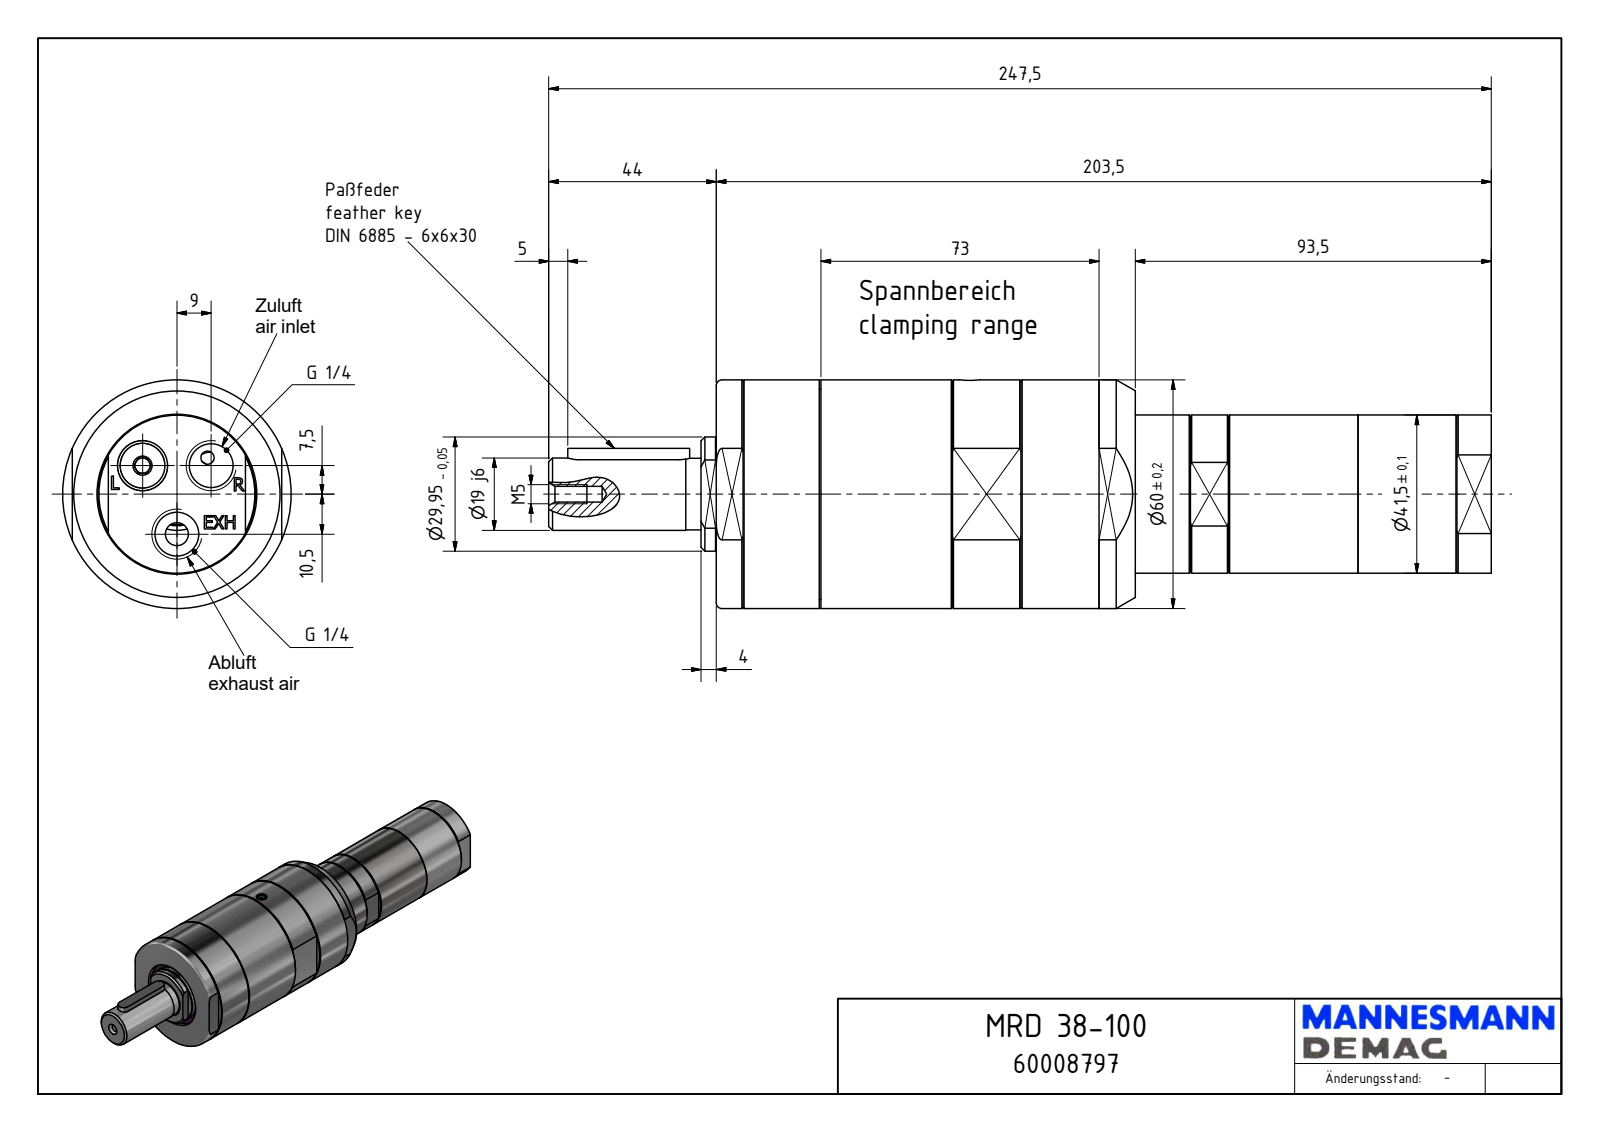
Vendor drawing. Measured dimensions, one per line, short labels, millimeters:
name: MRD 38-100_60008797
written by: Autodesk Inventor 2018 (AUTOMOTIVE_DESIGN)
unit: mm
bodies: 1 solid, 215 faces (125 planar, 41 cylindrical, 49 other)
size: 247.5 × 60 × 60
volume: 443 336 mm³; area: 45 818 mm²
holes: 3× ⌀11.45, 2× ⌀4, 1× ⌀1.55, 1× ⌀4.13, 1× ⌀5.5, 1× ⌀35, 1× ⌀42
bosses: 1× ⌀60, 1× ⌀55.18, 1× ⌀41.5, 1× ⌀39, 1× ⌀29.95, 1× ⌀19, 1× ⌀18.8, 1× ⌀5
rounds: 2× R3, 1× R26.55, 1× R28.45
face distances: 93.5, 203.5, 110, 55, 1, 27.5, 82.5, 176, 9.5, 31
hole spacings: 11.72, 20.12, 10.5, 18
